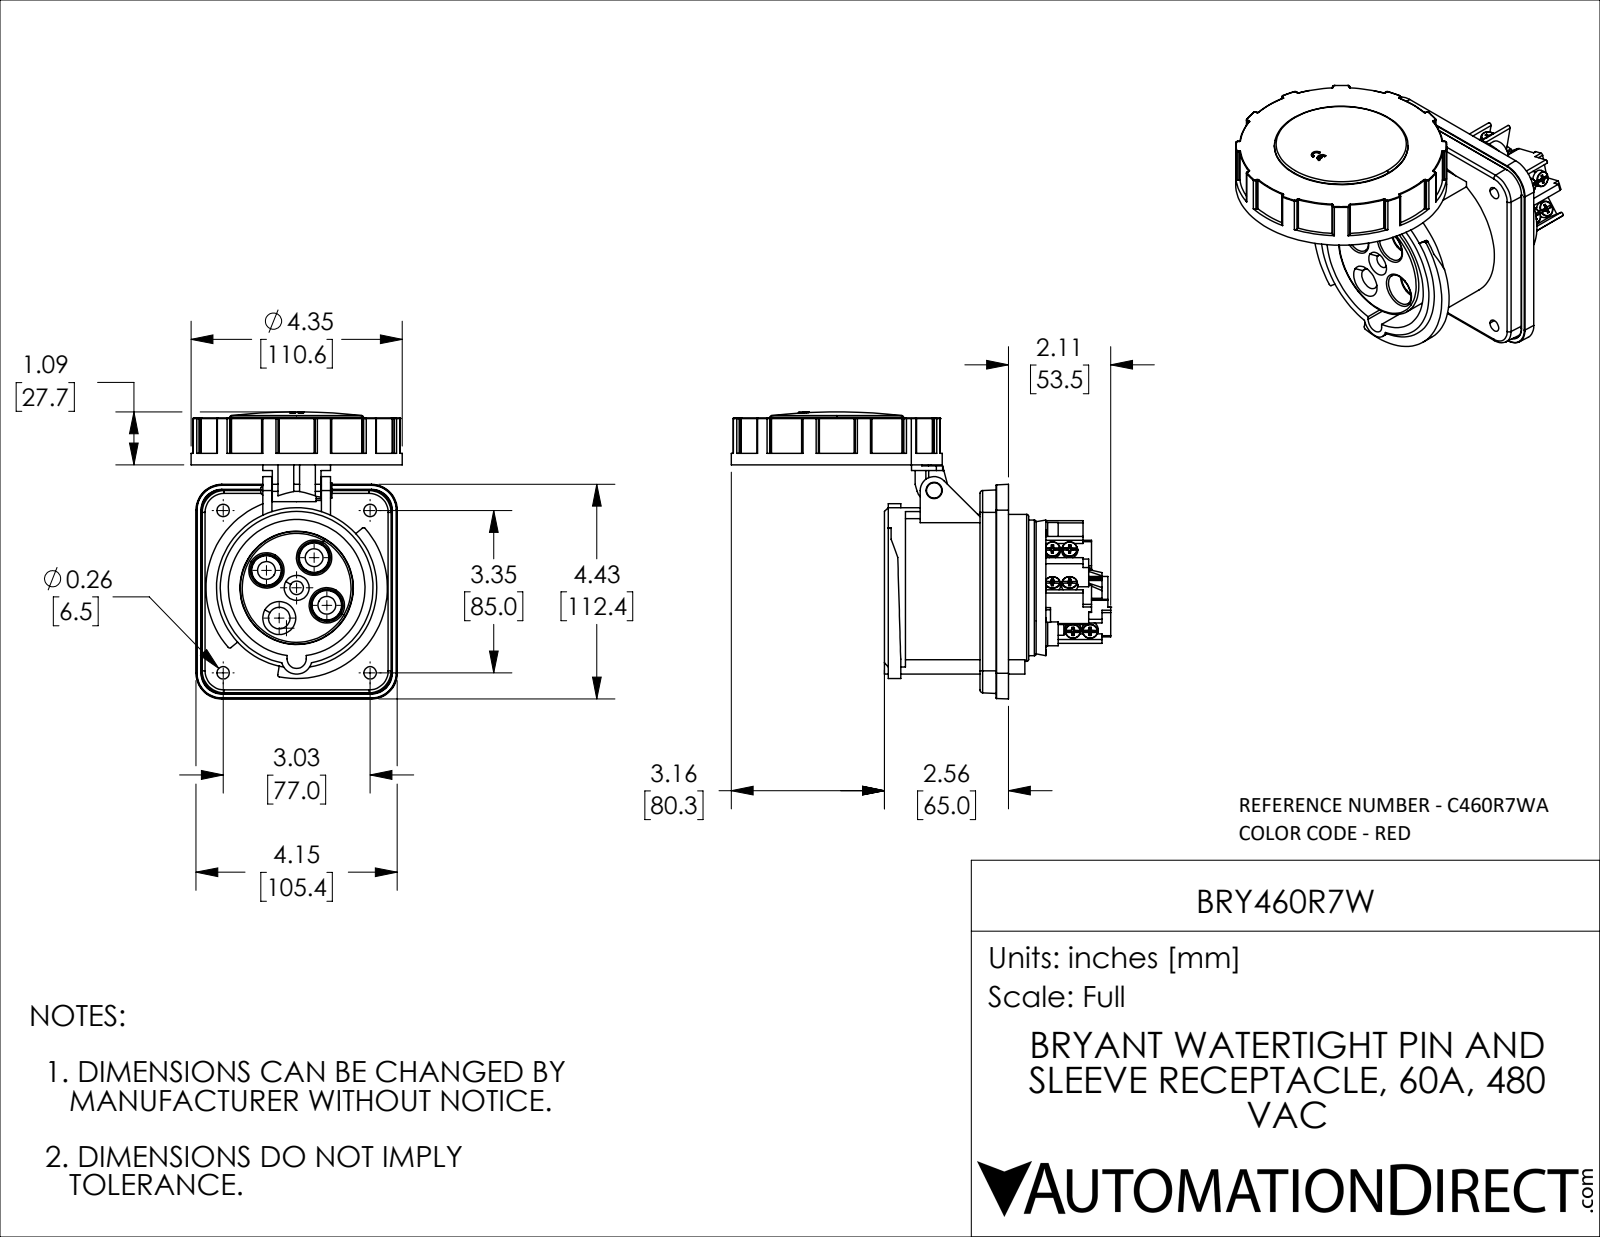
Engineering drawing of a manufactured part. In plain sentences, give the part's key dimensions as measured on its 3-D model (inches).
The part is named "BRY460R7W". Its 3-D file was written by "SolidWorks 2021 (CONFIG_CONTROL_DESIGN)". It is 2 solids with 1651 faces: 654 planar, 556 cylindrical and 441 other. Overall it measures 7.826 by 5.919 by 4.352 inches. Its volume is 40.79 cubic inches and its surface area 202.8 square inches. Round holes: 4 of diameter 0.256, 3 of diameter 0.354, 3 of diameter 0.366, 1 of diameter 0.118, 1 of diameter 0.197, 1 of diameter 0.201, 1 of diameter 0.28, 1 of diameter 0.335, 1 of diameter 0.445, 1 of diameter 2.819, 1 of diameter 3.189, 1 of diameter 3.961. Round bosses or shafts: 9 of diameter 0.197, 1 of diameter 4.352, 1 of diameter 3.307, 1 of diameter 3.031, 1 of diameter 2.795, 1 of diameter 2.756, 1 of diameter 0.512, 1 of diameter 0.472. Partial cylindrical surfaces (rounded edges, fillets, slot ends): 85 of radius 0.02, 48 of radius 0.012, 45 of radius 0.039, 8 of radius 0.01, 8 of radius 0.098, 7 of radius 0.006, 6 of radius 0.04, 6 of radius 0.05. The main face-to-face distances are 0.591, 2.48, 0.768, 1.89, 0.118, 0.886, 0.079, 0.965, 2.303, 0.433. The hole center spacings are 0.718, 1.016, 1.093, 1.437, 2.2, 2.209, 2.308, 2.317.
